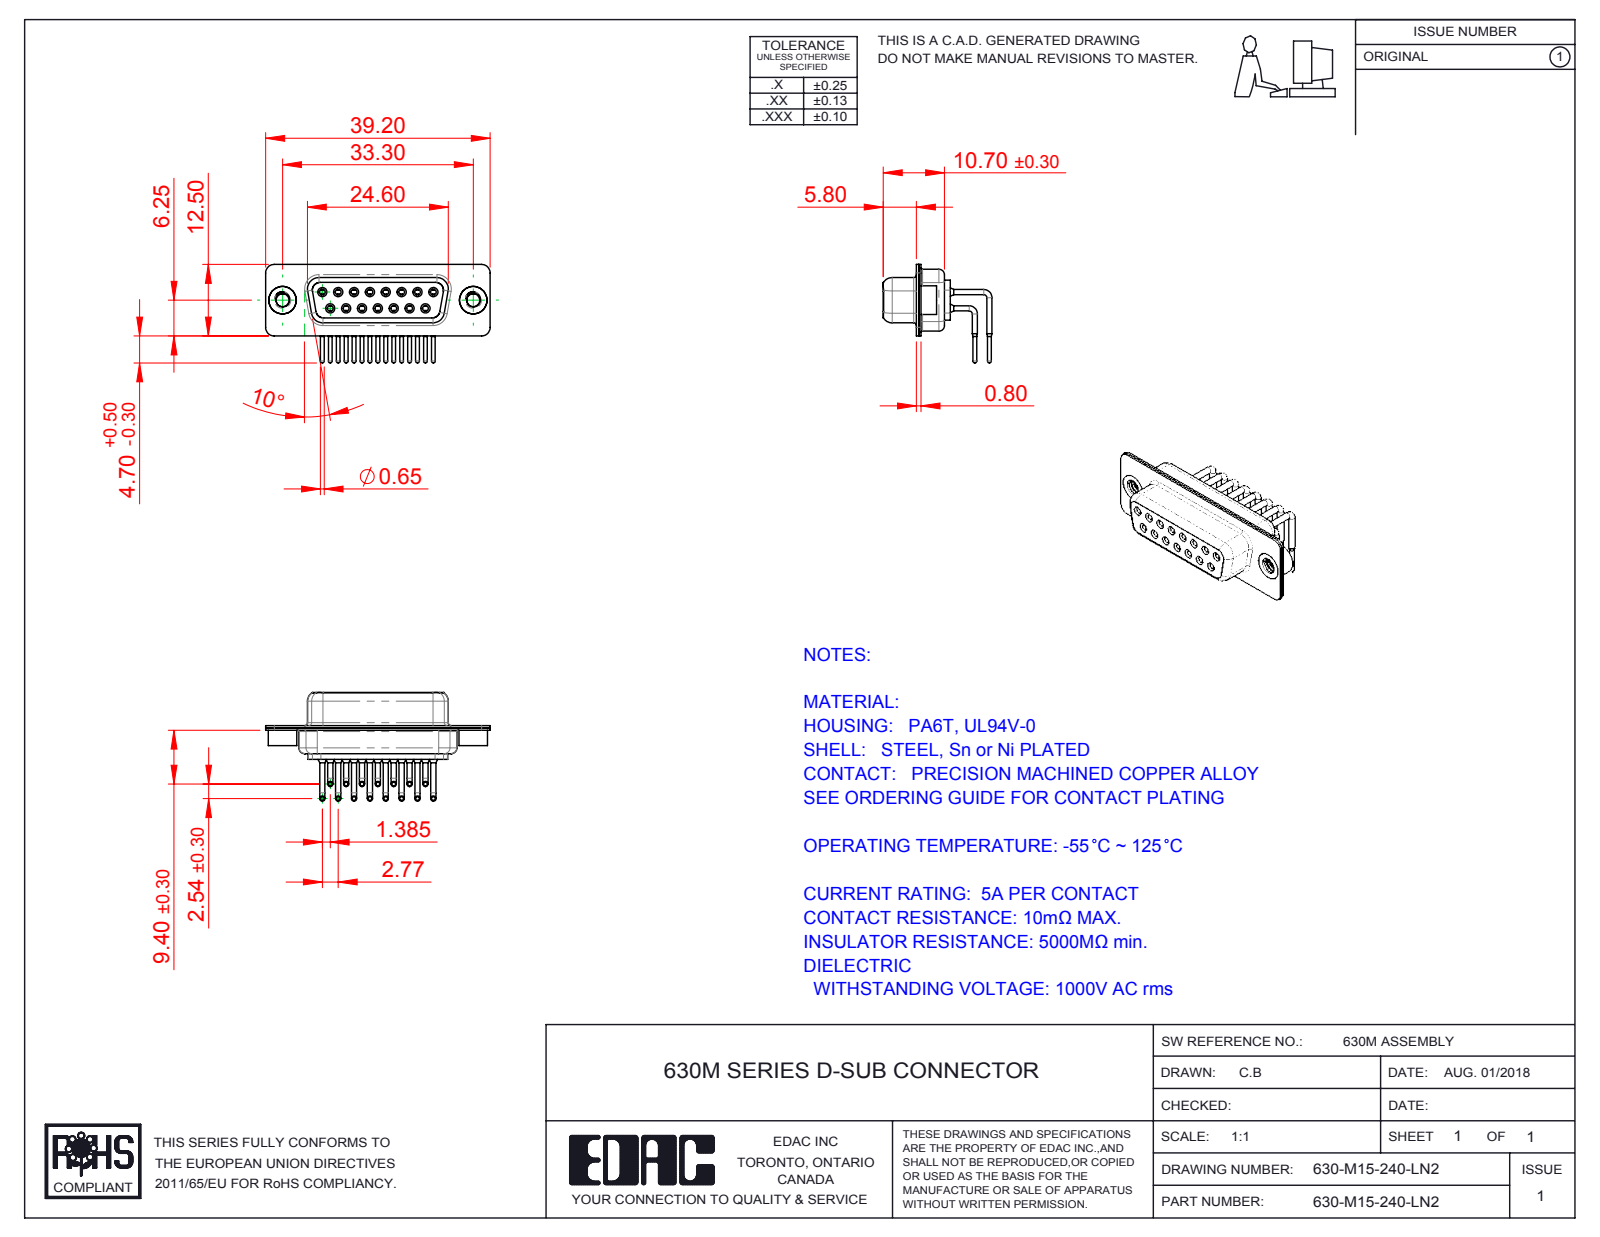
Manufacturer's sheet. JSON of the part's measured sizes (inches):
{"part_name": "630M Contact Row 2; 630M Shell Rear_15 Contacts; 630-M15-240-LN2; 630M Contact Row 1 (+3 more)", "step_written_by": "SolidWorks 2016 (CONFIG_CONTROL_DESIGN)", "units": "inches", "bodies": {"solids": 20, "faces": 1074, "planar": 292, "cylindrical": 482, "other": 300}, "overall_size": [1.543, 0.748, 0.677], "volume_in3": 0.157, "surface_area_in2": 10.16, "round_holes": [[0.039, 15], [0.043, 15], [0.067, 15], [0.071, 15], [0.079, 15], [0.089, 2], [0.157, 2], [0.189, 2]], "round_bosses_or_shafts": [[0.035, 30], [0.063, 15], [0.059, 15], [0.026, 15], [0.197, 2], [0.193, 2]], "partial_cylinders_radius": [[0.059, 16], [0.079, 12], [0.053, 8], [0.063, 8], [0.01, 4], [0.02, 4], [0.024, 4], [0.026, 4]], "face_to_face_distances": [0.016, 0.057, 0.352, 0.091, 0.244, 0.031, 0.075, 0.335, 0.018, 0.278], "hole_center_spacings": [0.124, 0.109, 0.218, 0.327, 0.436, 0.198, 0.198, 0.294]}
